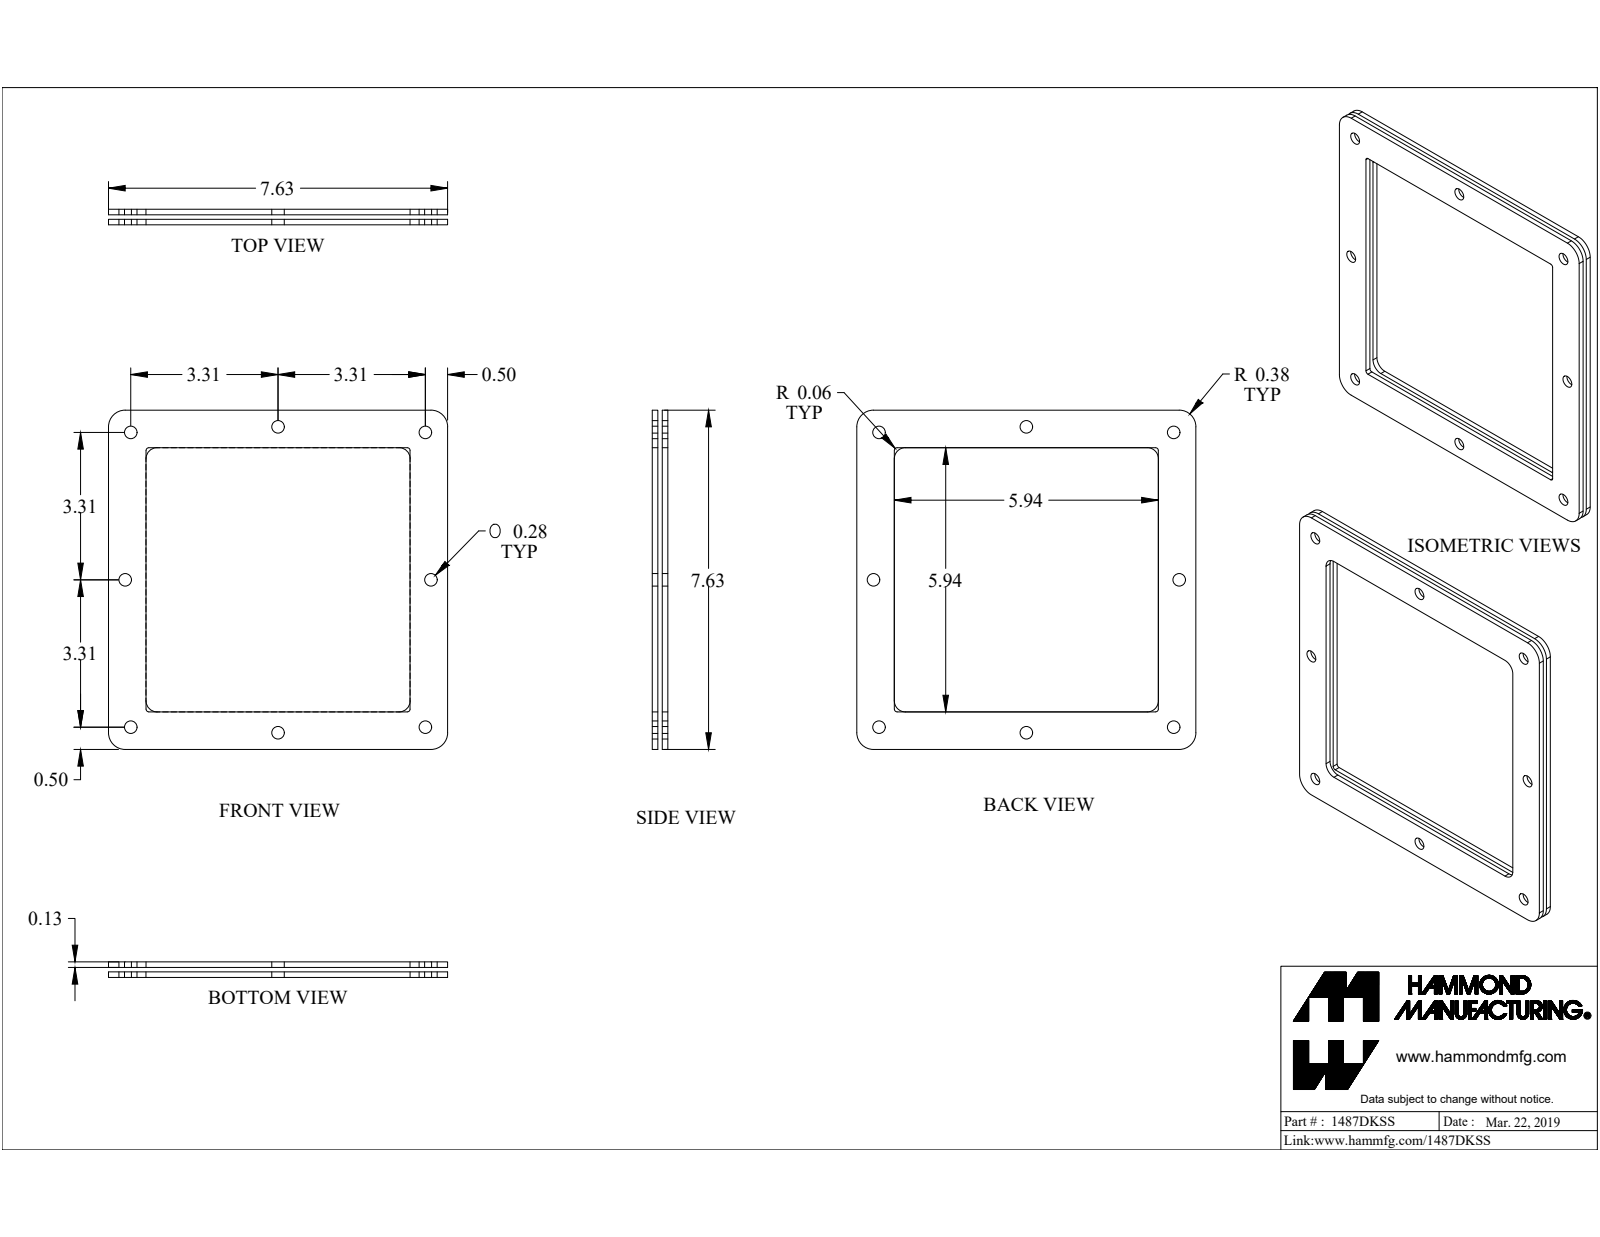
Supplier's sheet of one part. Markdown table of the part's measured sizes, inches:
| quantity | value |
| --- | --- |
| part name | 1487DKSS |
| STEP written by | SolidWorks 2019 (CONFIG_CONTROL_DESIGN) |
| units | inches |
| bodies | 7 solids, 217 faces (126 planar, 75 cylindrical, 16 other) |
| overall size | 7.625 × 7.625 × 1.916 |
| volume | 5.743 in³ |
| surface area | 108.4 in² |
| round holes (diameter × count) | 0.281 × 8, 0.258 × 2, 0.35 × 2, 0.196 × 1 |
| round bosses / shafts (diameter × count) | 0.5 × 2, 0.25 × 2 |
| partial cylindrical surfaces (radius × count) | 0.02 × 12, 0.25 × 5, 0.063 × 4, 0.375 × 4 |
| main face-to-face distances | 0.125, 0.1, 0.225, 0.225, 0.35, 0.125, 7.625, 0.844, 6.781, 0.843 |
| hole center spacings | 3.315, 7.519, 3.437, 4.685, 4.861, 6.625, 6.875, 9.369 |
